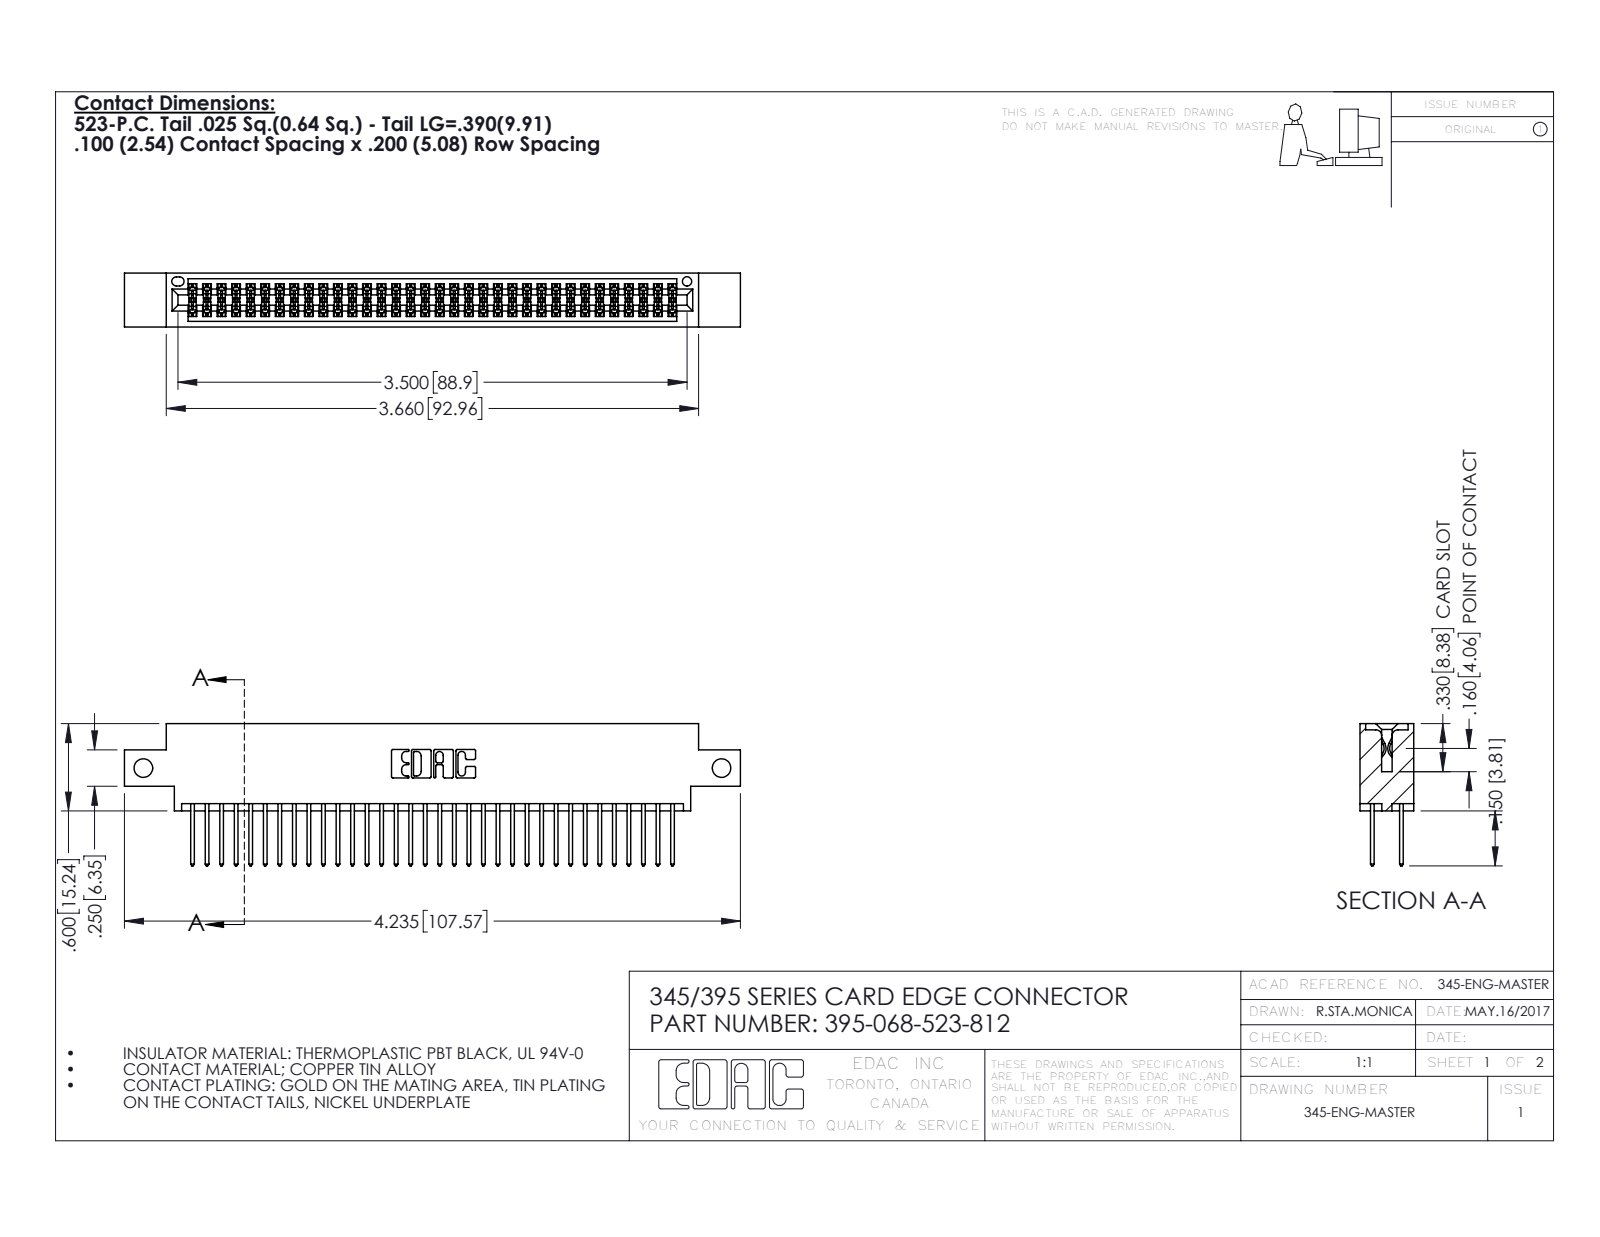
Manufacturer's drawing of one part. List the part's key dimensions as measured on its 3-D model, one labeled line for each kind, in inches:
Part name (STEP PRODUCT): 345-292-001_345-293-123; 345 Part_0.170 Offset - Side Mount; 395-068-523-812
STEP written by: SolidWorks 2016 (CONFIG_CONTROL_DESIGN)
Units: inches
Bodies: 69 solids, 3530 faces (2328 planar, 1202 cylindrical, 0 other)
Overall size (bounding box): 4.235 × 0.977 × 0.37
Volume: 0.629 in³ · Surface area: 24.37 in²
Round holes (diameter × count): ⌀0.128 ×2, ⌀0.064 ×1
Partial cylindrical surfaces — rounded edges, fillets, slot ends (radius × count): R0.006 ×102, R0.01 ×68, R0.01 ×22, R0.007 ×6, R0.031 ×6, R0.026 ×3, R0.014 ×2, R0.019 ×2
Main face-to-face distances: 0.298, 0.072, 0.2, 0.098, 0.272, 0.025, 0.37, 0.225, 0.175, 0.149
Hole centre spacings: 3.975
